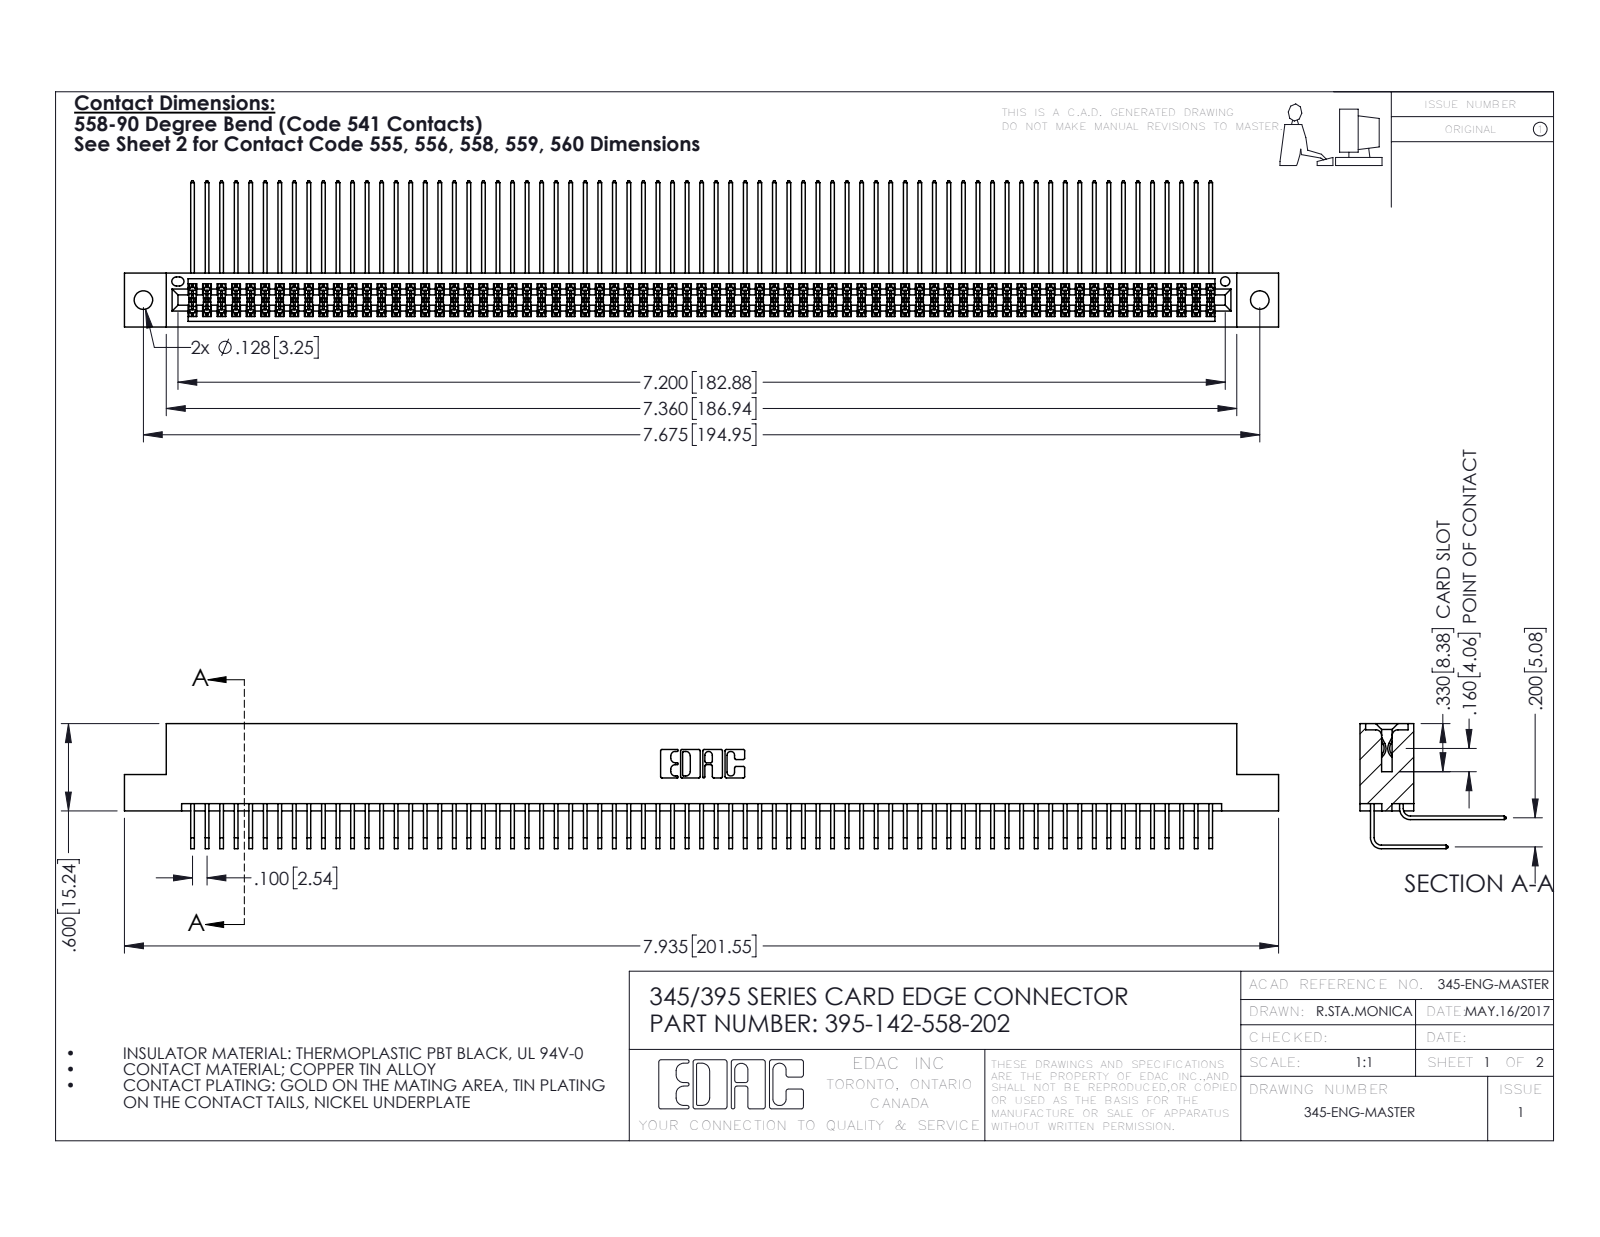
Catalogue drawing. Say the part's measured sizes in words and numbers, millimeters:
The part is named "345 Part_Flush Mounting Lugs - 0.128 Dia; 345-292-001_558 559 Tail - 1; 345-292-001_558 Tail - 2; 395-142-558-202". Its 3-D file was written by "SolidWorks 2016 (CONFIG_CONTROL_DESIGN)". It is 143 solids with 7510 faces: 5050 planar, 2460 cylindrical and 0 other. Overall it measures 201.5 by 25.5 by 21.8 millimeters. Its volume is 20 630 cubic millimeters and its surface area 34 640 square millimeters. Round holes: 2 of diameter 3.3, 1 of diameter 1.6. Partial cylindrical surfaces (rounded edges, fillets, slot ends): 283 of radius 0.2, 22 of radius 0.3, 6 of radius 0.2, 6 of radius 0.8, 3 of radius 0.7, 2 of radius 0.4, 2 of radius 0.5, 2 of radius 0.6. The main face-to-face distances are 1.8, 7.6, 5.1, 9.4, 2.5, 6.9, 0.6, 5.7, 0.6, 4.4. The hole center spacings are 6.9, 189, 194.9.
